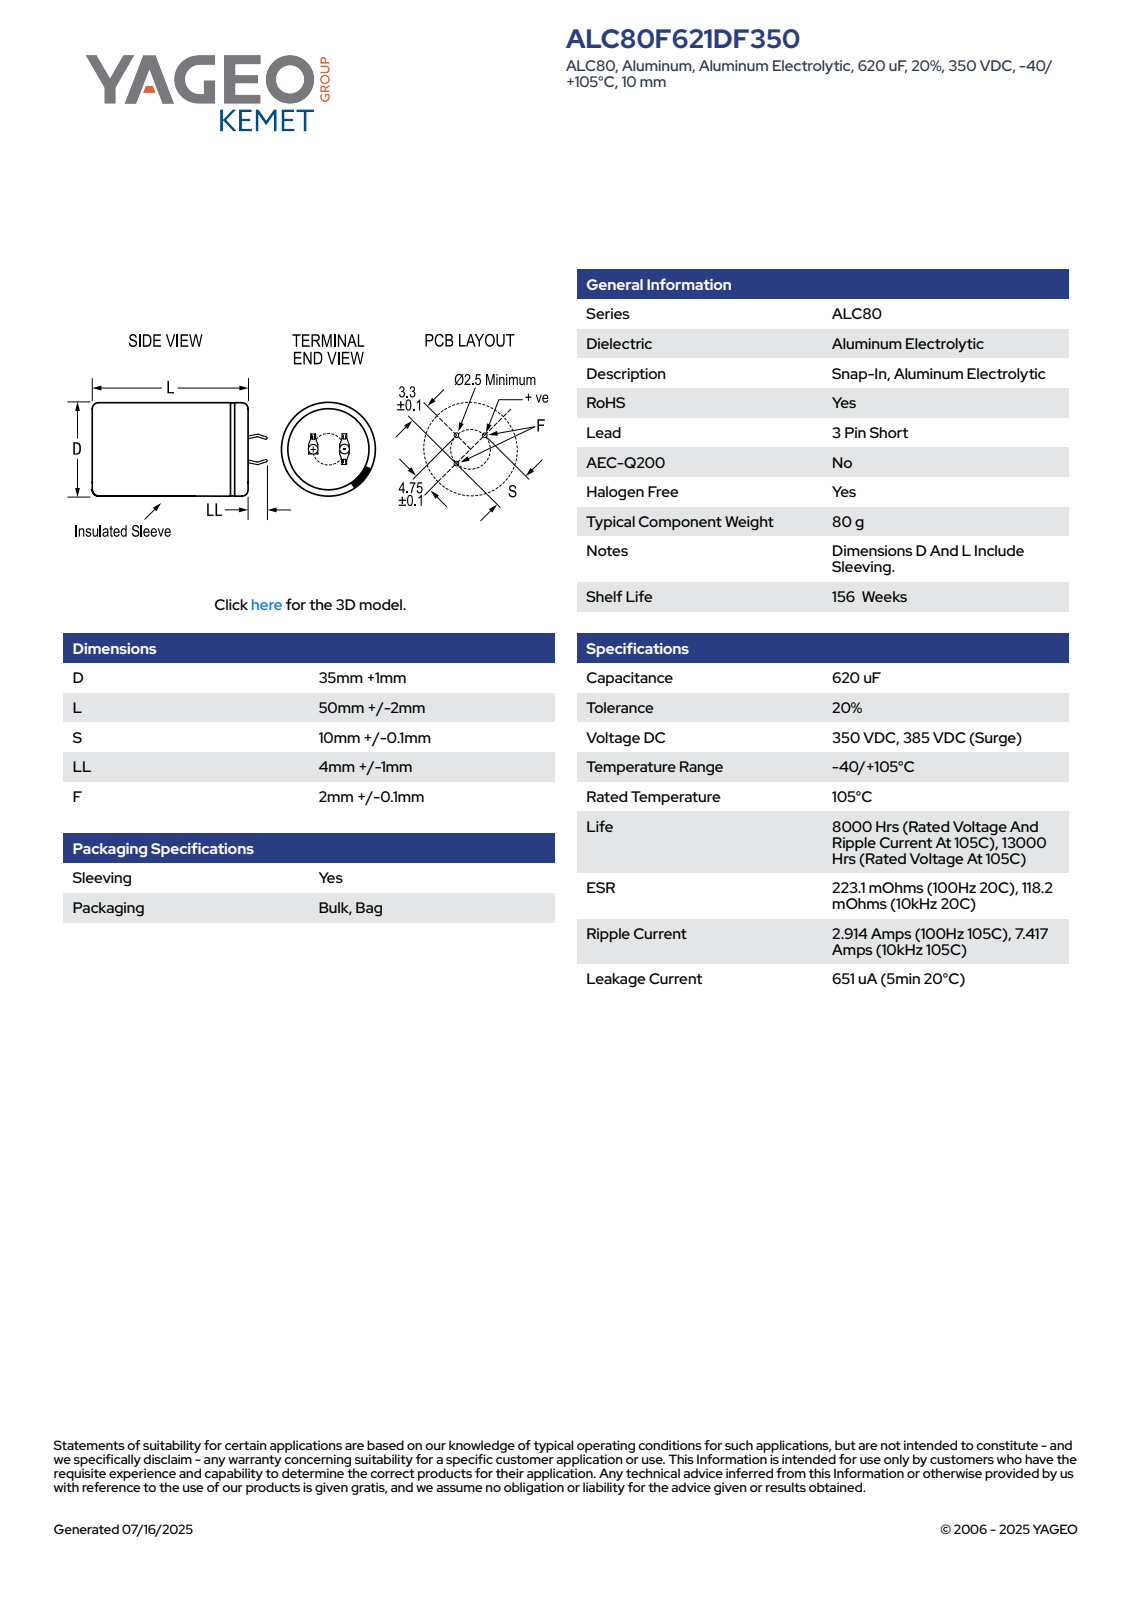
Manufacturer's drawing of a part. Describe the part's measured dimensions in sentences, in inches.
The part is named "CARS_K3P_35X50_D36L52S10LL5F2.1". Its 3-D file was written by "SolidWorks 2014 (AUTOMOTIVE_DESIGN)". It is 1 solid with 115 faces: 61 planar, 15 cylindrical and 39 other. Overall it measures 2.244 by 1.417 by 1.417 inches. Its volume is 3.198 cubic inches and its surface area 12.27 square inches. Round holes: 1 of diameter 1.254. Round bosses or shafts: 1 of diameter 1.417. Partial cylindrical surfaces (rounded edges, fillets, slot ends): 1 of radius 0.708. The main face-to-face distances are 2.047, 2.067, 0.02, 0.024, 0.324, 0.023, 0.03, 0.053, 0.256, 0.083.
